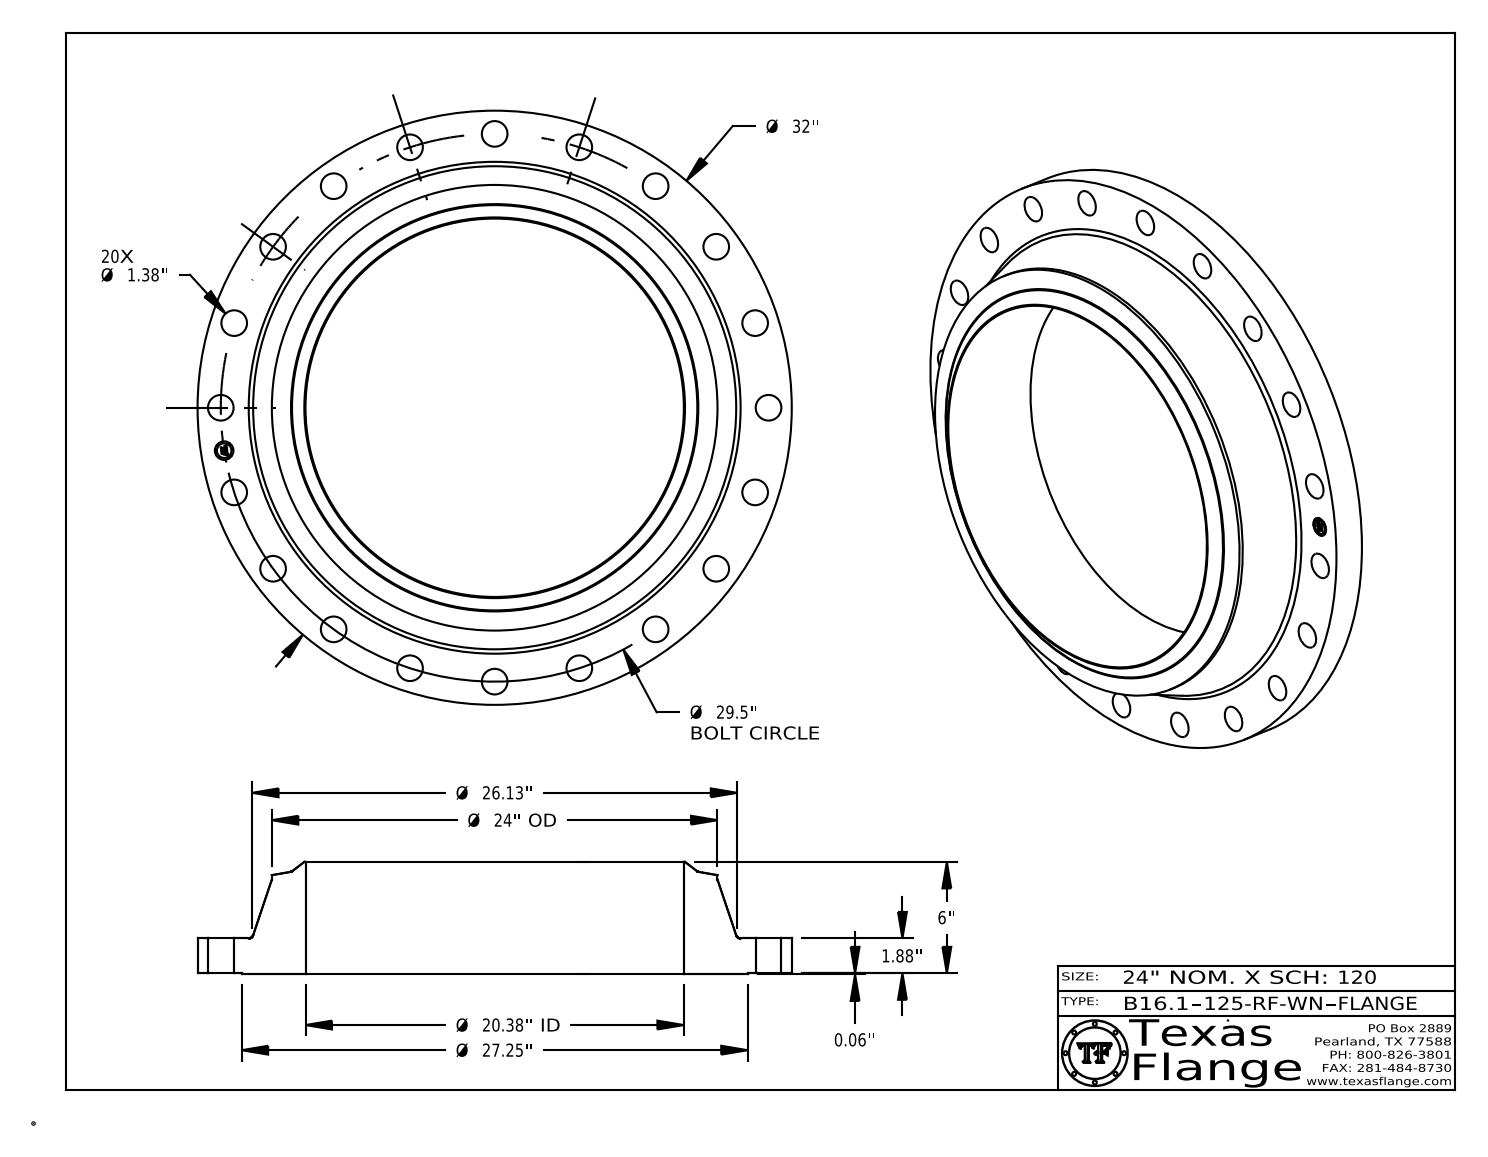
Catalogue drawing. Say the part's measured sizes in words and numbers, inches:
The part is named "B16.1, Class 125-RF-WN". Its 3-D file was written by "CATIA V5 STEP AP214 (AUTOMOTIVE_DESIGN)". It is 1 solid with 447 faces: 369 planar, 68 cylindrical and 10 other. Overall it measures 32 by 32 by 6.063 inches. Its volume is 1 451 cubic inches and its surface area 1 849 square inches. Round holes: 20 of diameter 1.38, 1 of diameter 1, 1 of diameter 20.376. Round bosses or shafts: 8 of diameter 0.061, 1 of diameter 32, 1 of diameter 27.25, 1 of diameter 24, 1 of diameter 0.788. The main face-to-face distances are 1.943, 0.063, 1.88, 6.063, 6, 4.12, 1.928, 1.865, 0.015, 4.135. The hole center spacings are 14.75, 29.137, 4.615, 17.34, 20.859, 23.866, 26.285, 9.116.
